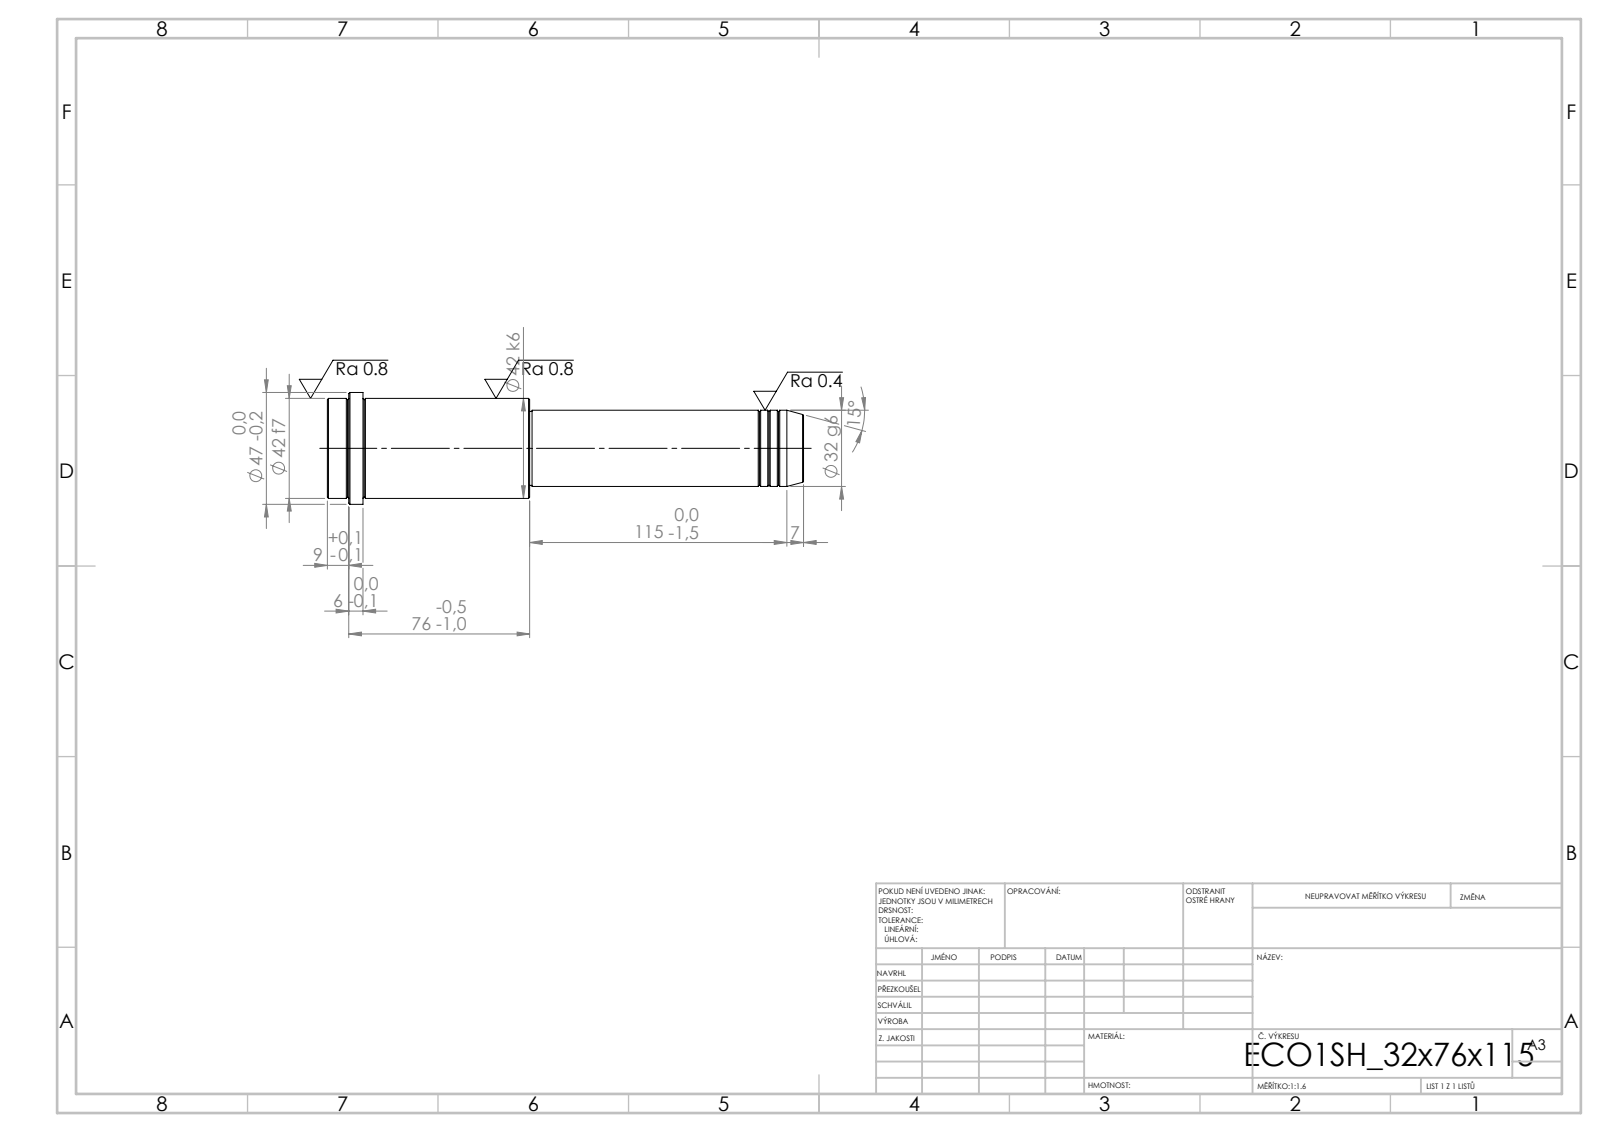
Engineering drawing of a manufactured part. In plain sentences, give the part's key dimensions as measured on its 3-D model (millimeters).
Its 3-D file was written by "SolidWorks 2019 (CONFIG_CONTROL_DESIGN)". It is 1 solid with 52 faces: 6 planar, 16 cylindrical and 30 other. Overall it measures 200 by 47 by 47 millimeters. Its volume is 211 391 cubic millimeters and its surface area 26 417 square millimeters. Round bosses or shafts: 1 of diameter 47, 1 of diameter 42, 1 of diameter 32, 1 of diameter 31. The main face-to-face distances are 200, 115, 85, 185, 70, 15, 191, 76, 6, 9.
